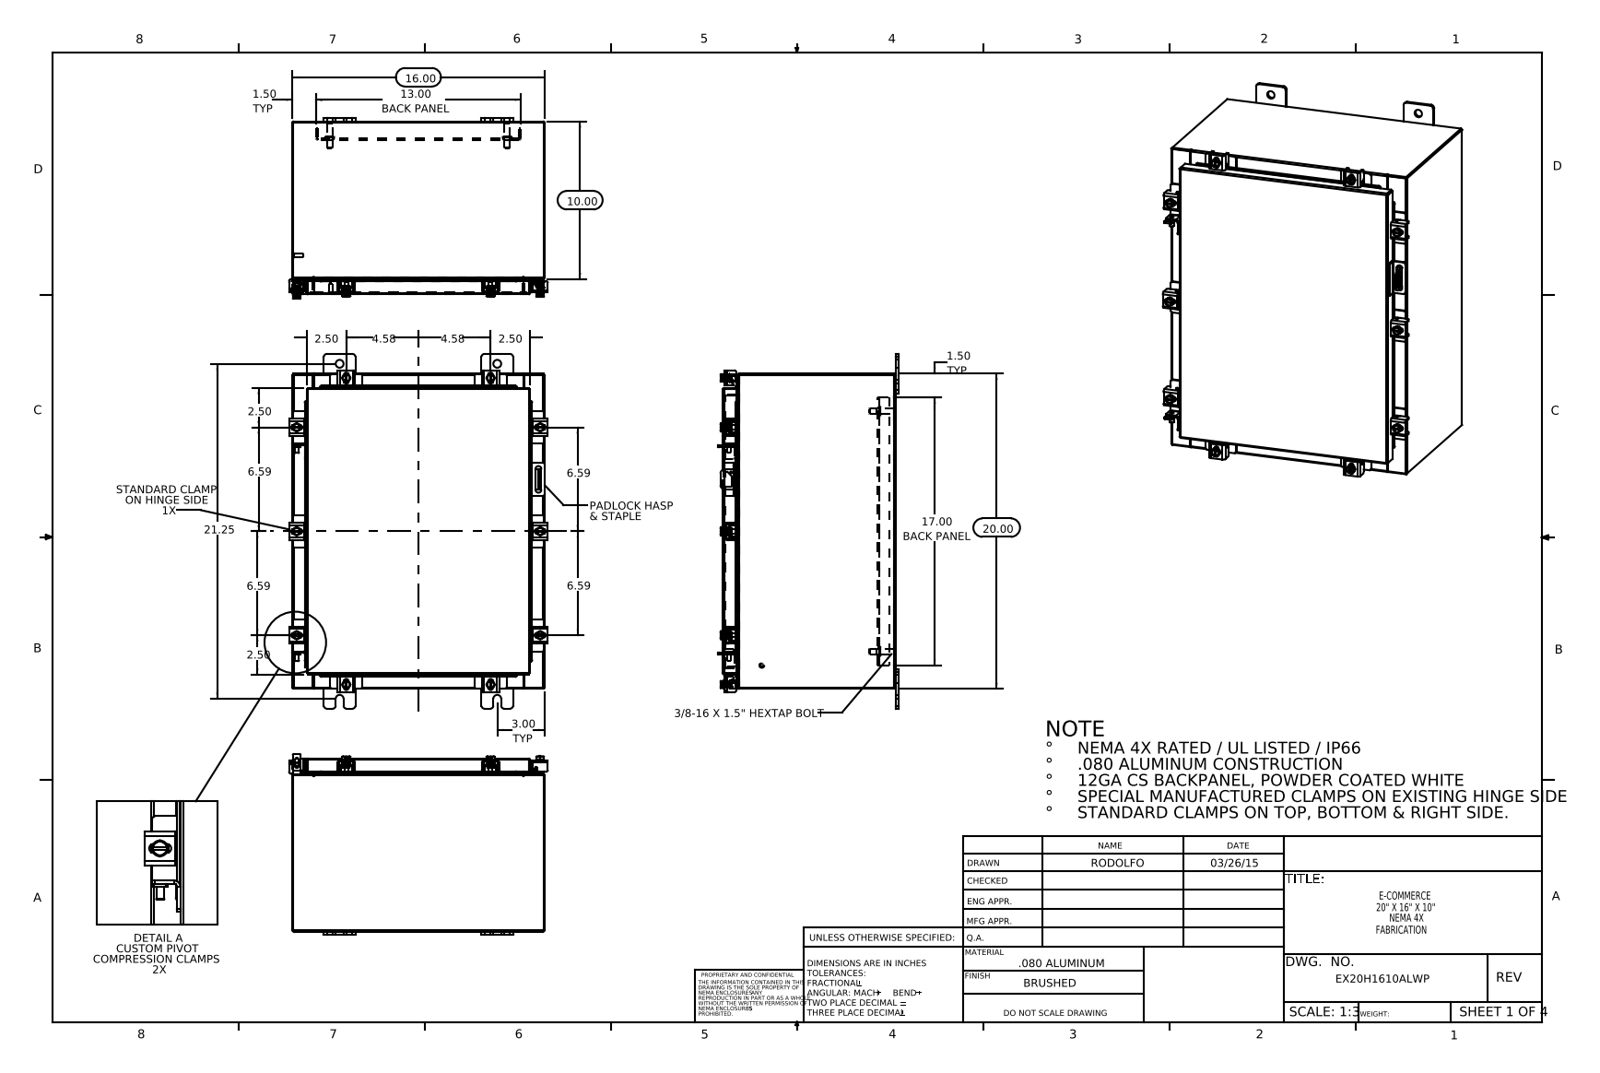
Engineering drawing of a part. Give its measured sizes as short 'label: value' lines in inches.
name: EX20H1610ALWP Body; EX20H1610ALWP Bottom; EX20H1610ALWP Padlock Staple; EX20H1610ALWP Standard Clamps (+8 more)
written by: SolidWorks 2014 (CONFIG_CONTROL_DESIGN)
unit: in
bodies: 71 solids, 1784 faces (955 planar, 685 cylindrical, 144 other)
size: 22.5 × 16.421 × 11.453
volume: 146.1 in³; area: 3 692 in²
holes: 10× ⌀0.213, 10× ⌀0.26, 8× ⌀0.5, 1× ⌀0.125, 1× ⌀0.25
bosses: 10× ⌀0.5, 10× ⌀0.25, 8× ⌀0.399, 4× ⌀0.625, 4× ⌀0.375, 4× ⌀0.33, 2× ⌀0.315, 2× ⌀0.236
rounds: 46× R0.06, 24× R0.013, 24× R0.19, 22× R0.088, 20× R0.141, 18× R0.12, 16× R0.09, 16× R0.1
face distances: 0.075, 10.9, 15.925, 19.925, 10.975, 10.826, 0.104, 1, 1.075, 9.826
hole spacings: 2.347, 4.44, 6.594, 10.222, 12.696, 14.374, 15.683, 16.62
